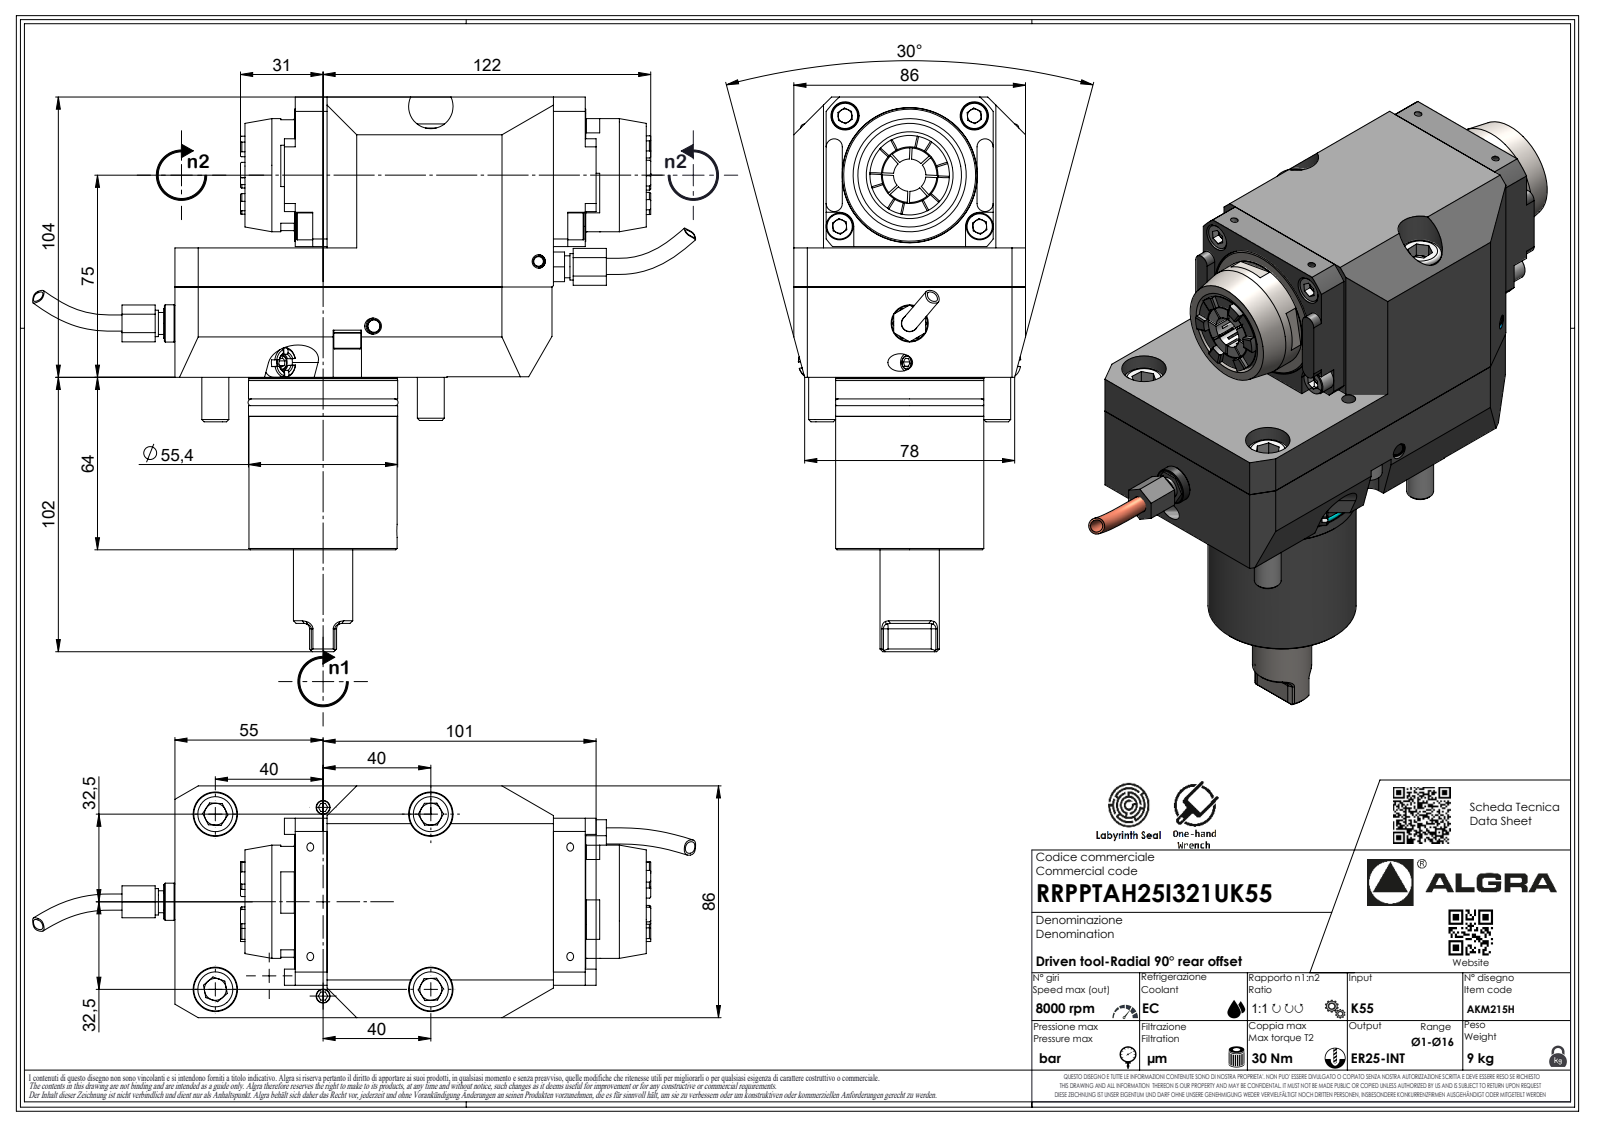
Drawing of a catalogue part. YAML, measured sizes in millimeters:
part_name: "RRPPTAH25I321UK55"
step_written_by: "SolidWorks 2023 (AUTOMOTIVE_DESIGN)"
units: millimeters
bodies: {solids: 1, faces: 509, planar: 345, cylindrical: 60, other: 104}
overall_size: [205.8, 175, 86]
volume: 1230000
surface_area: 84608
round_holes:
  - {diameter: 2.1, count: 1}
round_bosses_or_shafts:
  - {diameter: 55.39, count: 1}
  - {diameter: 55, count: 1}
  - {diameter: 54.99, count: 1}
  - {diameter: 51.5, count: 1}
  - {diameter: 42, count: 1}
  - {diameter: 22, count: 1}
  - {diameter: 6.37, count: 1}
  - {diameter: 1.7, count: 1}
partial_cylinders:
  - {radius: 0.33, count: 7}
  - {radius: 0.52, count: 7}
  - {radius: 3.7, count: 7}
  - {radius: 2, count: 6}
  - {radius: 3, count: 4}
  - {radius: 0.21, count: 1}
  - {radius: 25.1, count: 1}
  - {radius: 39, count: 1}
face_to_face_distances: [86, 56, 104, 48, 12, 74, 0.5, 47.8, 103.8, 112]
